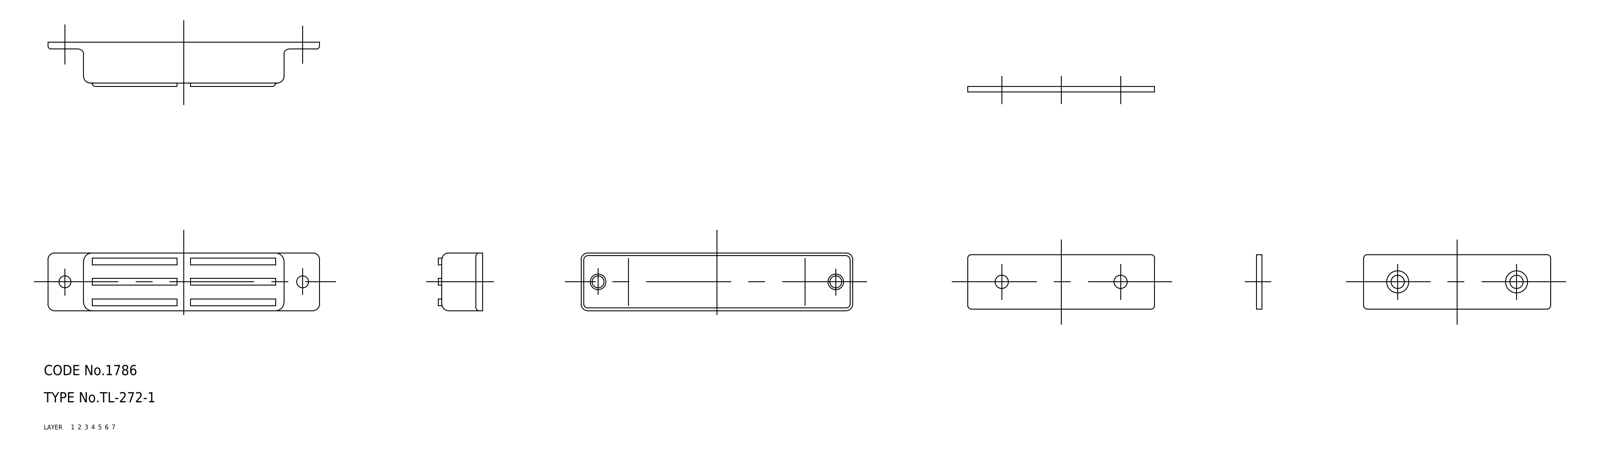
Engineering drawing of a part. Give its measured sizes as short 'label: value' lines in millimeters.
name: attachment; keeper; housing; base (+1 more)
written by: CADfix (AUTOMOTIVE_DESIGN)
unit: mm
bodies: 9 solids, 163 faces (0 planar, 0 cylindrical, 163 other)
size: 80 × 39.71 × 17
volume: 7 587 mm³; area: 13 978 mm²
